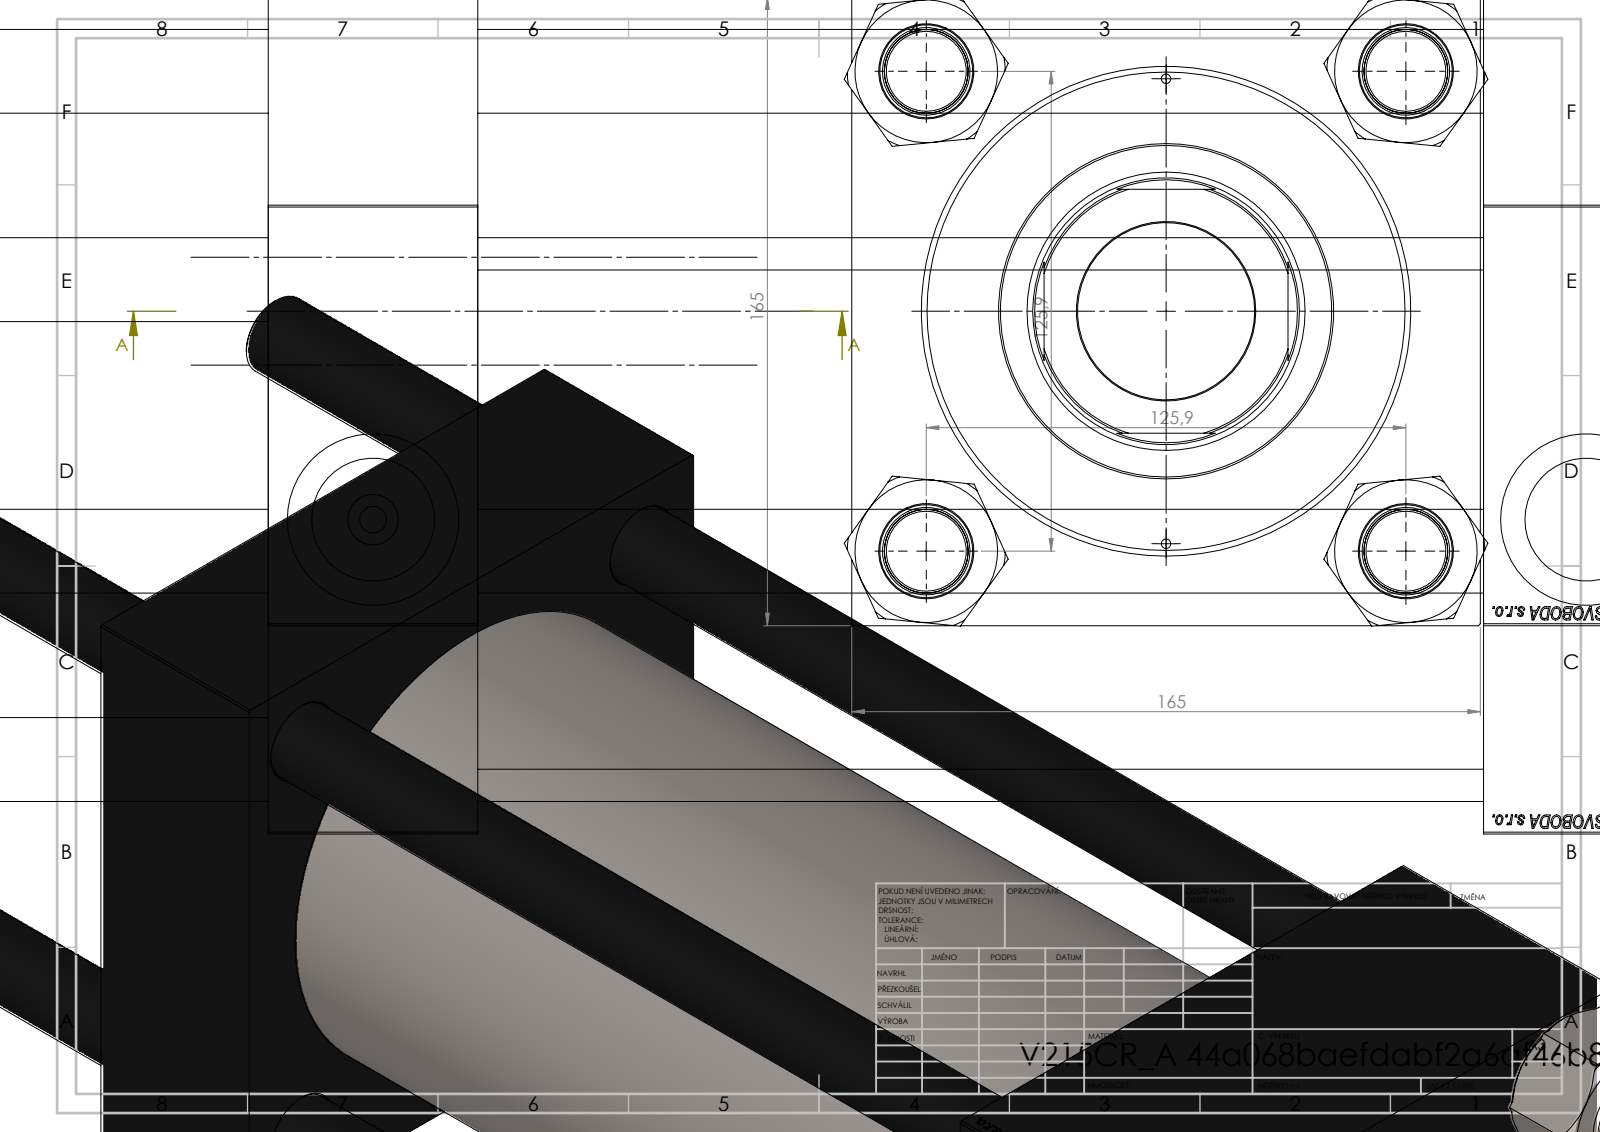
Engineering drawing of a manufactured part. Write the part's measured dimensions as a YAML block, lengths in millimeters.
part_name: "V215_VC_A; V215CR_VCP; CR025_012_A_0_G_A_G_M_020_+#_##_TYCINKA; V215CR_BODY_A (+1 more)"
step_written_by: "SolidWorks 2019 (CONFIG_CONTROL_DESIGN)"
units: millimeters
bodies: {solids: 11, faces: 1188, planar: 570, cylindrical: 82, other: 536}
overall_size: [513, 168.94, 165.27]
volume: 5973000
surface_area: 790283
round_holes:
  - {diameter: 22, count: 4}
  - {diameter: 2.5, count: 2}
  - {diameter: 7, count: 2}
  - {diameter: 32.24, count: 2}
  - {diameter: 45, count: 2}
  - {diameter: 46.5, count: 1}
  - {diameter: 70, count: 1}
  - {diameter: 73, count: 1}
  - {diameter: 96, count: 1}
  - {diameter: 125, count: 1}
  - {diameter: 125.5, count: 1}
round_bosses_or_shafts:
  - {diameter: 25, count: 4}
  - {diameter: 131, count: 1}
  - {diameter: 88, count: 1}
partial_cylinders:
  - {radius: 34, count: 1}
face_to_face_distances: [165, 55, 397, 342, 319, 264, 78, 368.3, 313.3, 49.3]
hole_center_spacings: [62.98, 89.02, 125.9, 139.02, 61, 178.05, 122, 318.5]
